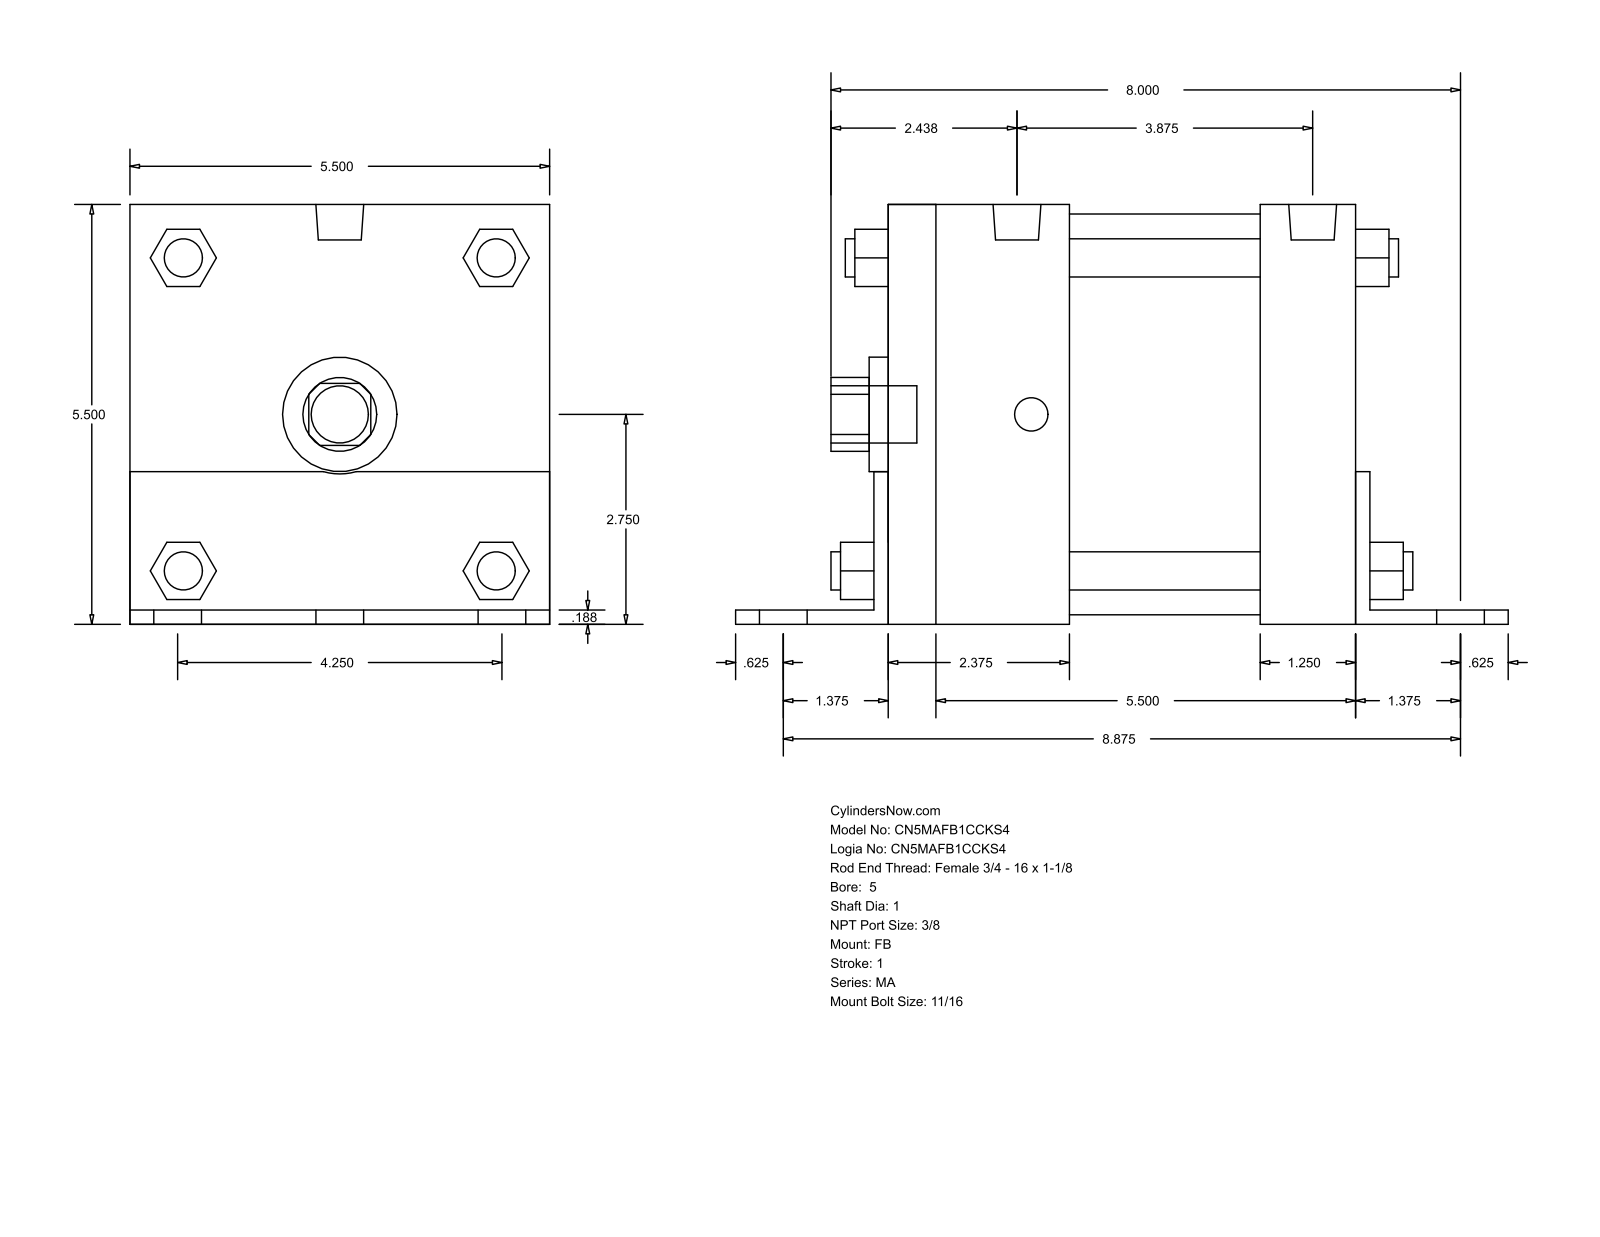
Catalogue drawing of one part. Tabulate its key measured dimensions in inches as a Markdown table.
| quantity | value |
| --- | --- |
| part name | MA_FB__0500_1 |
| STEP written by | GSSL Pune (CONFIG_CONTROL_DESIGN) |
| units | inches |
| bodies | 0 solids, 140 faces (105 planar, 35 cylindrical, 0 other) |
| overall size | 10.125 × 5.502 × 5.5 |
| round holes (diameter × count) | 1 × 1, 1.5 × 1, 5.25 × 1 |
| round bosses / shafts (diameter × count) | 0.687 × 6, 0.5 × 4, 0.437 × 4, 0.627 × 2, 0.75 × 1 |
| partial cylindrical surfaces (radius × count) | 0.484 × 1, 0.78 × 1 |
| main face-to-face distances | 5.5, 0.187, 5.502, 0.185, 5.315, 6.125, 0.188, 6.313, 6.312, 6.5 |
